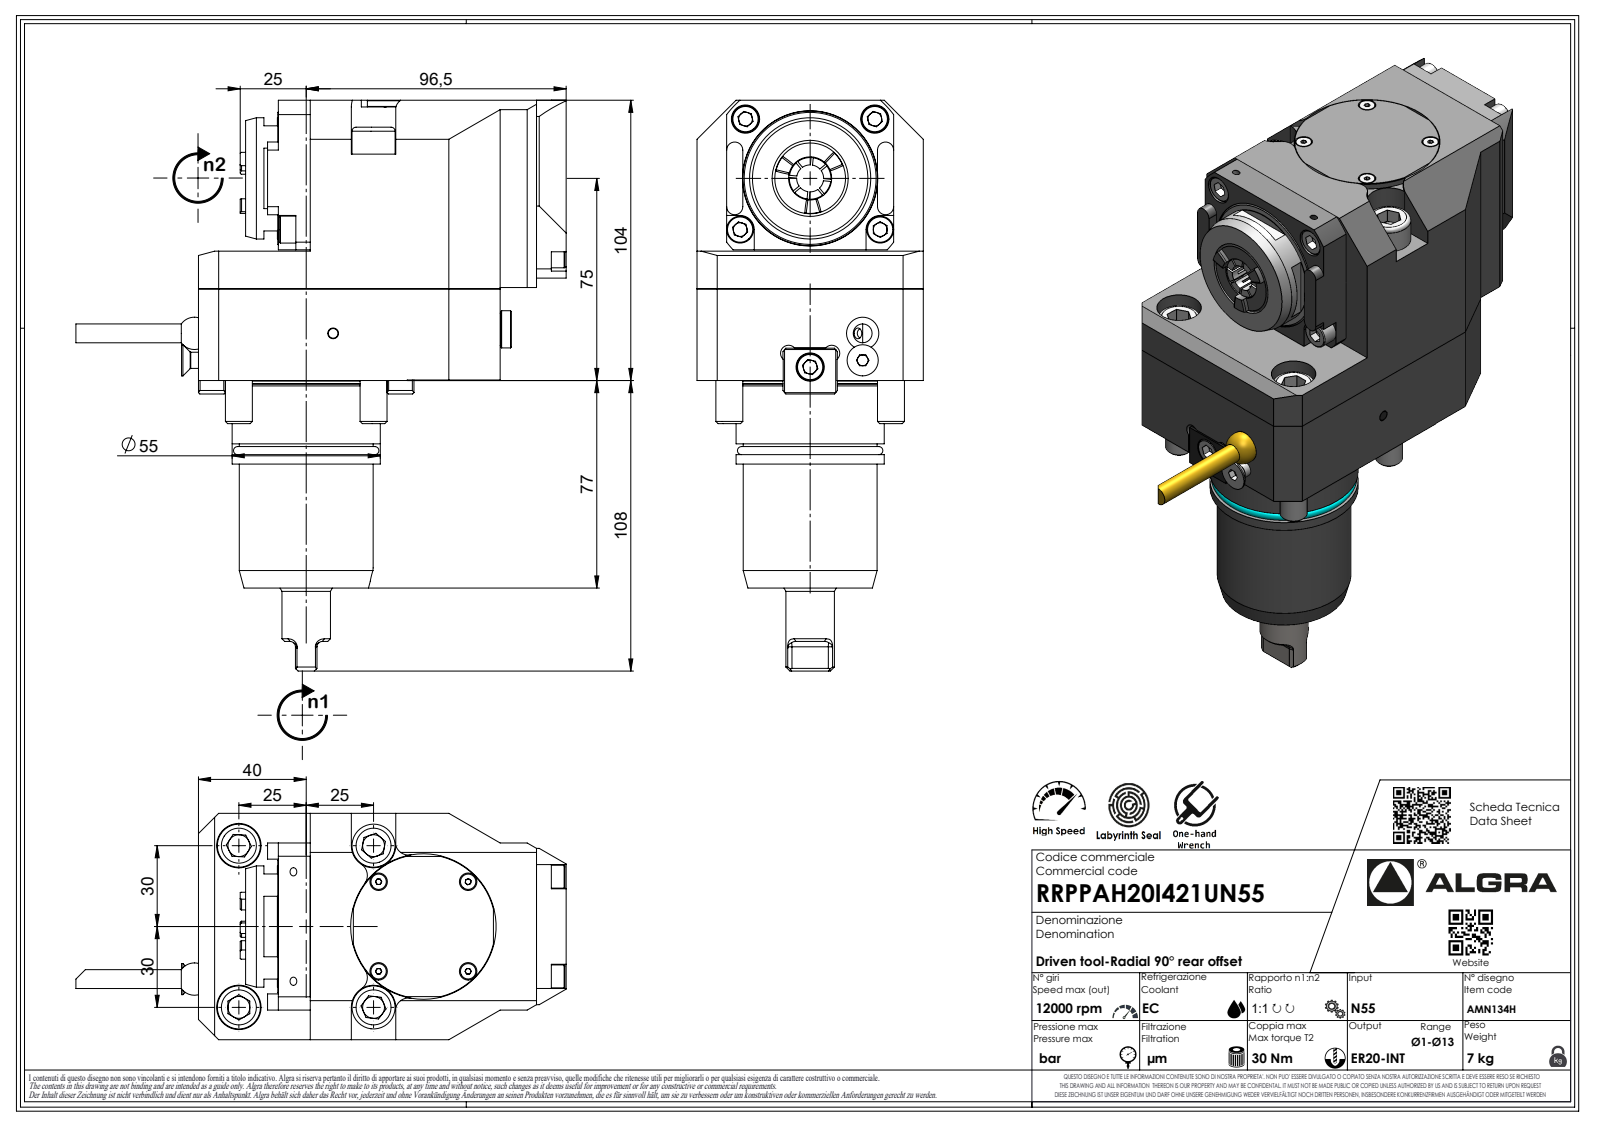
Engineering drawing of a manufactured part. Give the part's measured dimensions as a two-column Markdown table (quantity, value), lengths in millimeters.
| quantity | value |
| --- | --- |
| part name | RRPPAH20I421UN55 |
| STEP written by | SolidWorks 2023 (AUTOMOTIVE_DESIGN) |
| units | millimeters |
| bodies | 1 solid, 592 faces (394 planar, 84 cylindrical, 114 other) |
| overall size | 211.8 × 182 × 84 |
| volume | 1 067 000 mm³ |
| surface area | 84 347 mm² |
| round holes (diameter × count) | 16.5 × 2, 2.1 × 1, 4 × 1, 54 × 1 |
| round bosses / shafts (diameter × count) | 16 × 4, 10 × 4, 55 × 1, 54.6 × 1, 49.7 × 1, 45 × 1, 18 × 1, 7 × 1 |
| partial cylindrical surfaces (radius × count) | 0.33 × 7, 0.52 × 7, 2 × 7, 3.7 × 7, 3 × 4, 5 × 4, 8.25 × 3, 0.21 × 1 |
| main face-to-face distances | 84, 104, 11, 136.5, 73, 56, 48, 112, 24.5, 62 |
| hole center spacings | 74.78, 60 |
